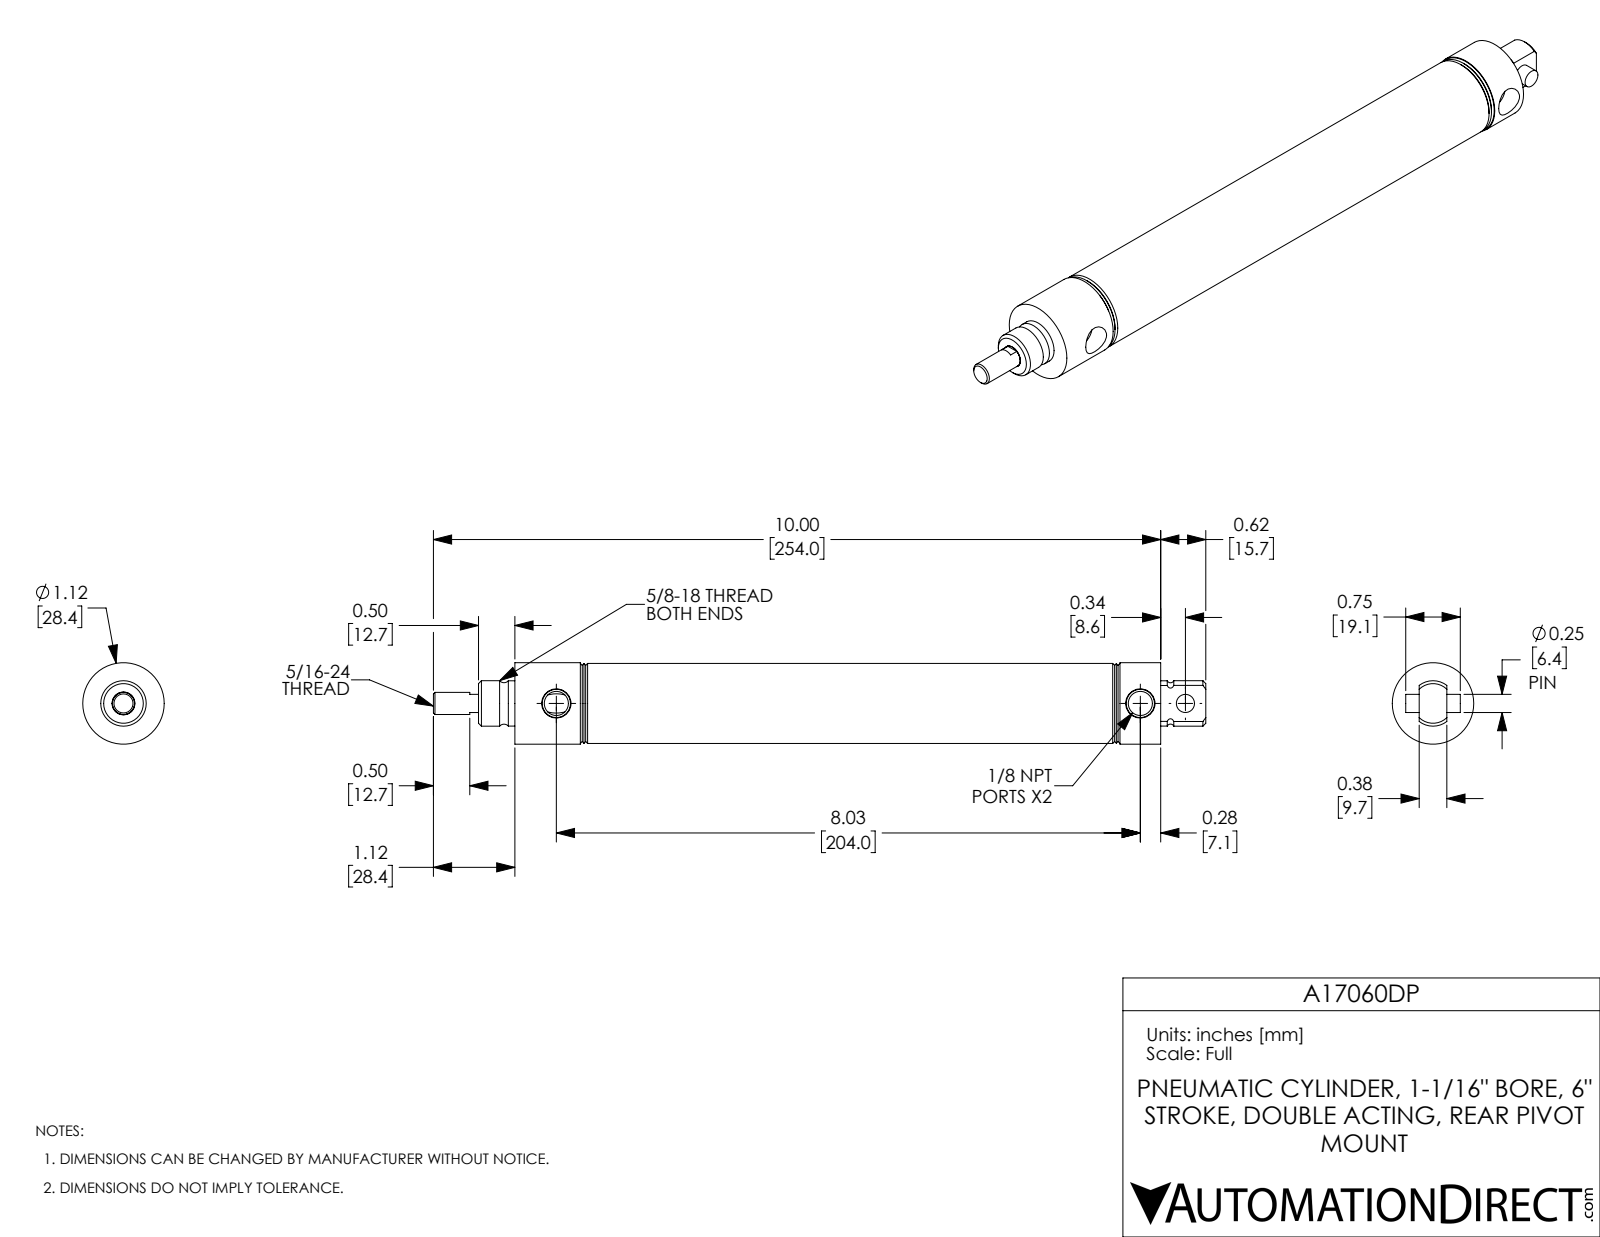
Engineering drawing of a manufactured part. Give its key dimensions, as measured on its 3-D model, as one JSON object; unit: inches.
{"part_name": "A17060DP; A17060DP-PIN; A17060DP-Rod; A17060DP-MainBody", "step_written_by": "SolidWorks 2017 (AUTOMOTIVE_DESIGN)", "units": "inches", "bodies": {"solids": 3, "faces": 92, "planar": 22, "cylindrical": 32, "other": 38}, "overall_size": [10.62, 1.12, 1.12], "volume_in3": 3.867, "surface_area_in2": 73.4, "round_holes": [[0.332, 2], [0.25, 1], [0.312, 1], [1.063, 1]], "round_bosses_or_shafts": [[1.12, 1], [1.1, 1], [0.625, 1], [0.623, 1], [0.304, 1]], "partial_cylinders_radius": [[0.313, 1]], "face_to_face_distances": [0.5, 7.69, 6.5, 6, 1.19, 1.69, 7.69, 8.88, 7.19, 1.19], "hole_center_spacings": [0.62, 8.03, 8.65]}
